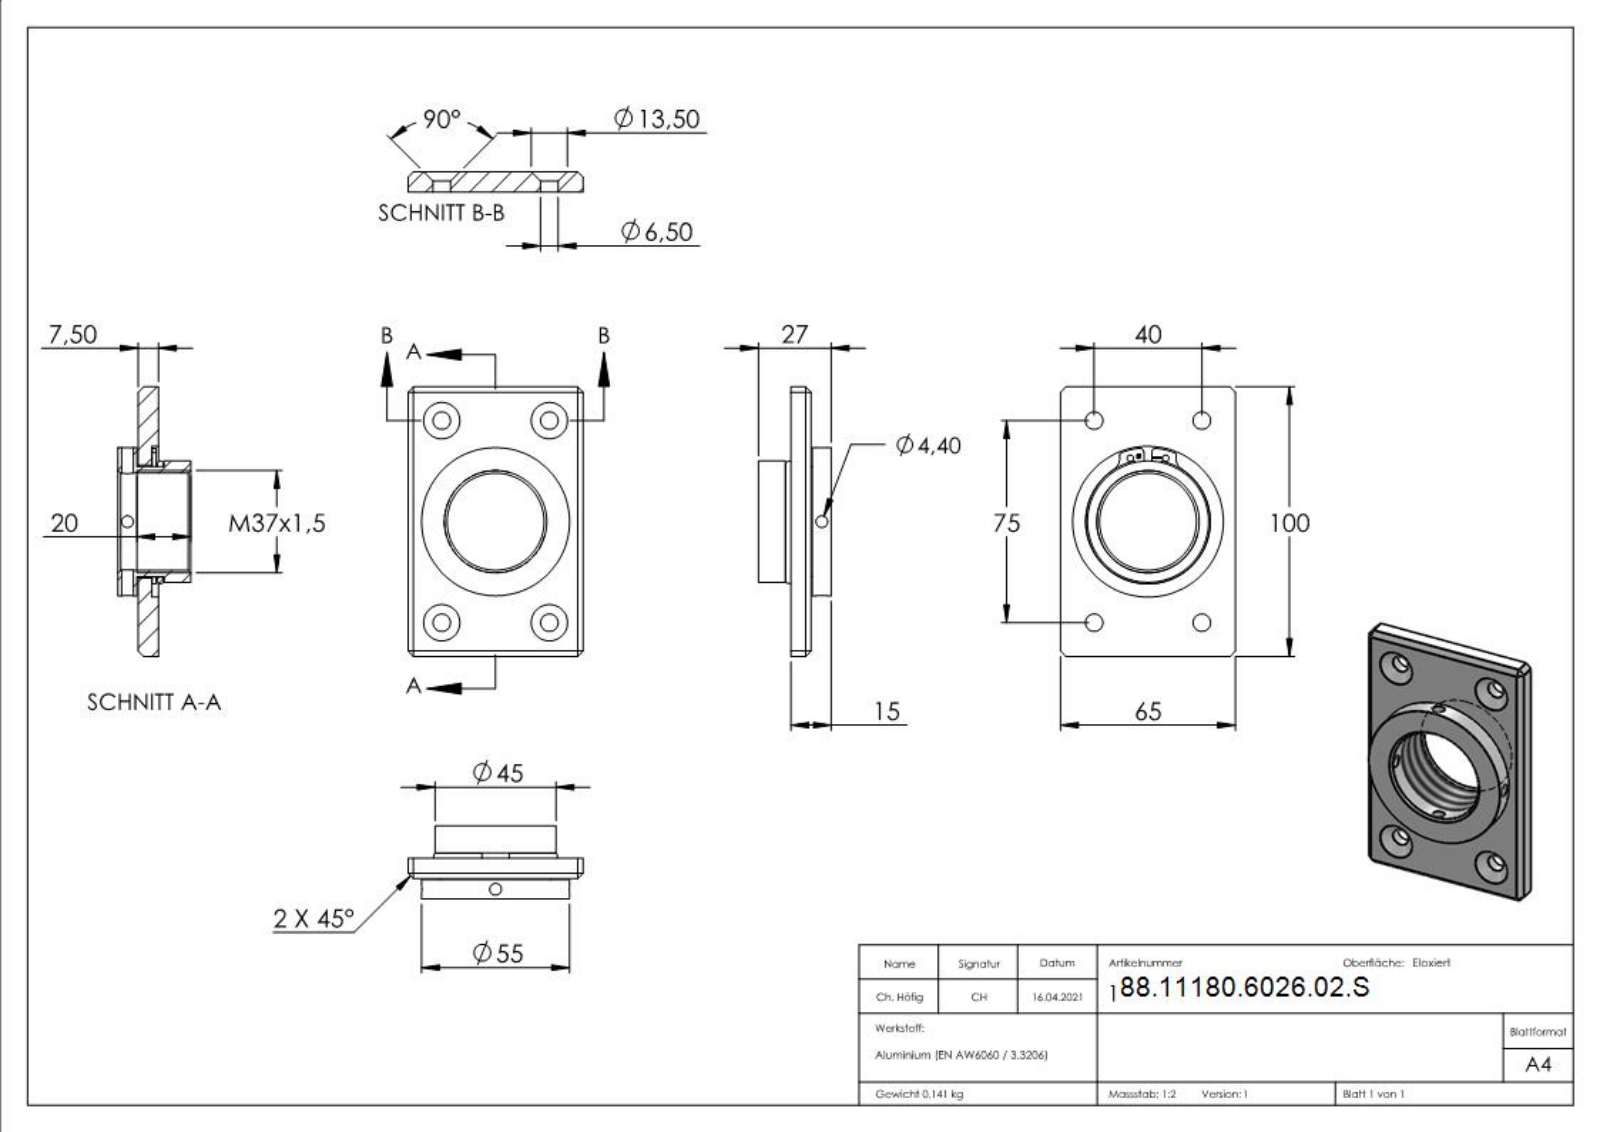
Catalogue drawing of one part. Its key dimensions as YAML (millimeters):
part_name: "180-6026-02-S"
step_written_by: "SolidWorks 2018 (CONFIG_CONTROL_DESIGN)"
units: millimeters
bodies: {solids: 4, faces: 394, planar: 173, cylindrical: 48, other: 173}
overall_size: [100, 65, 27]
volume: 52213
surface_area: 26408
round_holes:
  - {diameter: 6.5, count: 4}
  - {diameter: 2.4, count: 2}
  - {diameter: 4.4, count: 2}
  - {diameter: 36, count: 1}
  - {diameter: 41.1, count: 1}
  - {diameter: 42, count: 1}
  - {diameter: 56, count: 1}
round_bosses_or_shafts:
  - {diameter: 55, count: 1}
  - {diameter: 46.3, count: 1}
  - {diameter: 45, count: 1}
  - {diameter: 41, count: 1}
partial_cylinders:
  - {radius: 1, count: 2}
  - {radius: 1.5, count: 2}
  - {radius: 5, count: 2}
  - {radius: 27.4, count: 1}
face_to_face_distances: [7.5, 15, 5.1, 2.4, 12.6, 0.5, 8, 5.6, 7, 10]
hole_center_spacings: [42.5, 19.36, 24.45, 30.02, 40, 62.51, 66.59, 75]
